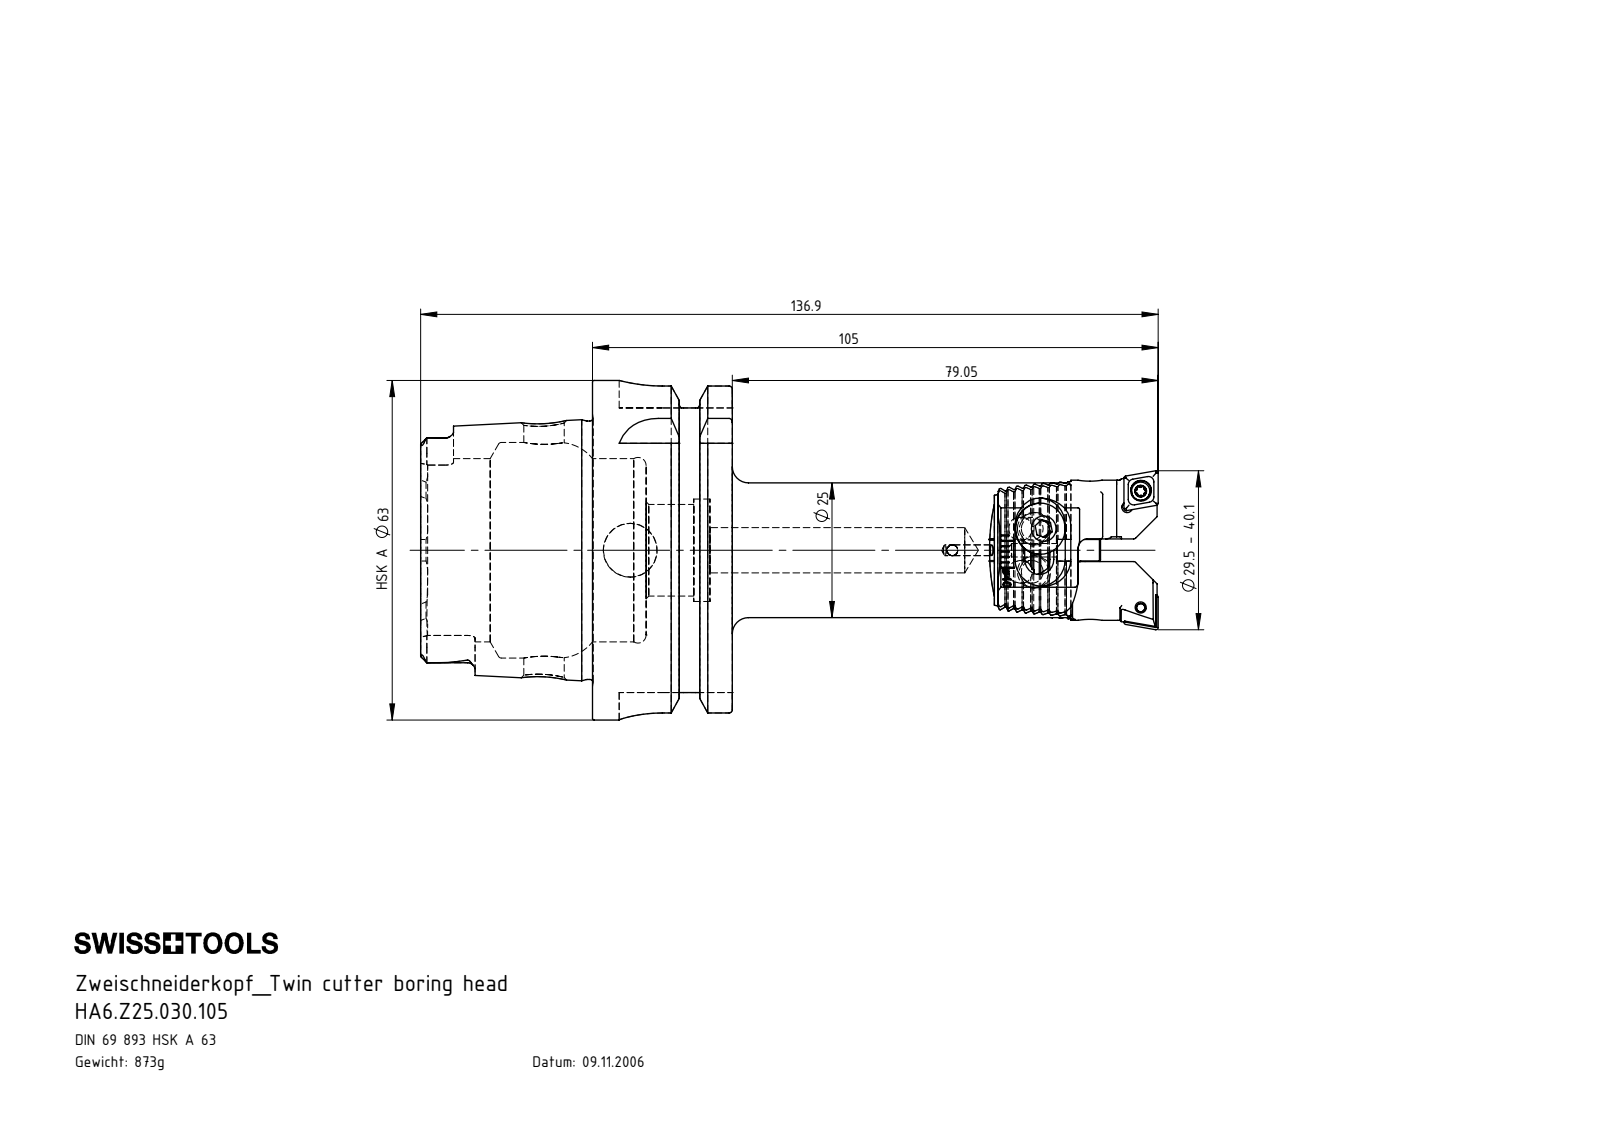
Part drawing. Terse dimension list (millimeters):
name: Z25-ER1.001.012; Z20-ER2.001.013_A; Z25-ER1.003.012_A_gespannt; Z25-ER1.002.012_A (+2 more)
written by: SolidWorks 2017 (AUTOMOTIVE_DESIGN)
unit: mm
bodies: 6 solids, 377 faces (210 planar, 90 cylindrical, 77 other)
size: 126.2 × 63 × 63
volume: 106 496 mm³; area: 29 963 mm²
holes: 4× ⌀2, 2× ⌀4.2, 2× ⌀5.3, 2× ⌀6, 1× ⌀2.5, 1× ⌀7.5, 1× ⌀8.4, 1× ⌀10, 1× ⌀17, 1× ⌀19, 1× ⌀34, 1× ⌀40
bosses: 2× ⌀9.5, 2× ⌀9.2, 2× ⌀5, 1× ⌀63, 1× ⌀54.95, 1× ⌀47.94, 1× ⌀25, 1× ⌀4
rounds: 18× R0.12, 6× R1.4, 4× R2.88, 4× R8, 2× R220
face distances: 25.95, 16, 1.43, 9.95, 52.8, 31.9, 41.85, 57.85, 2.86, 21.8
hole spacings: 59.8
